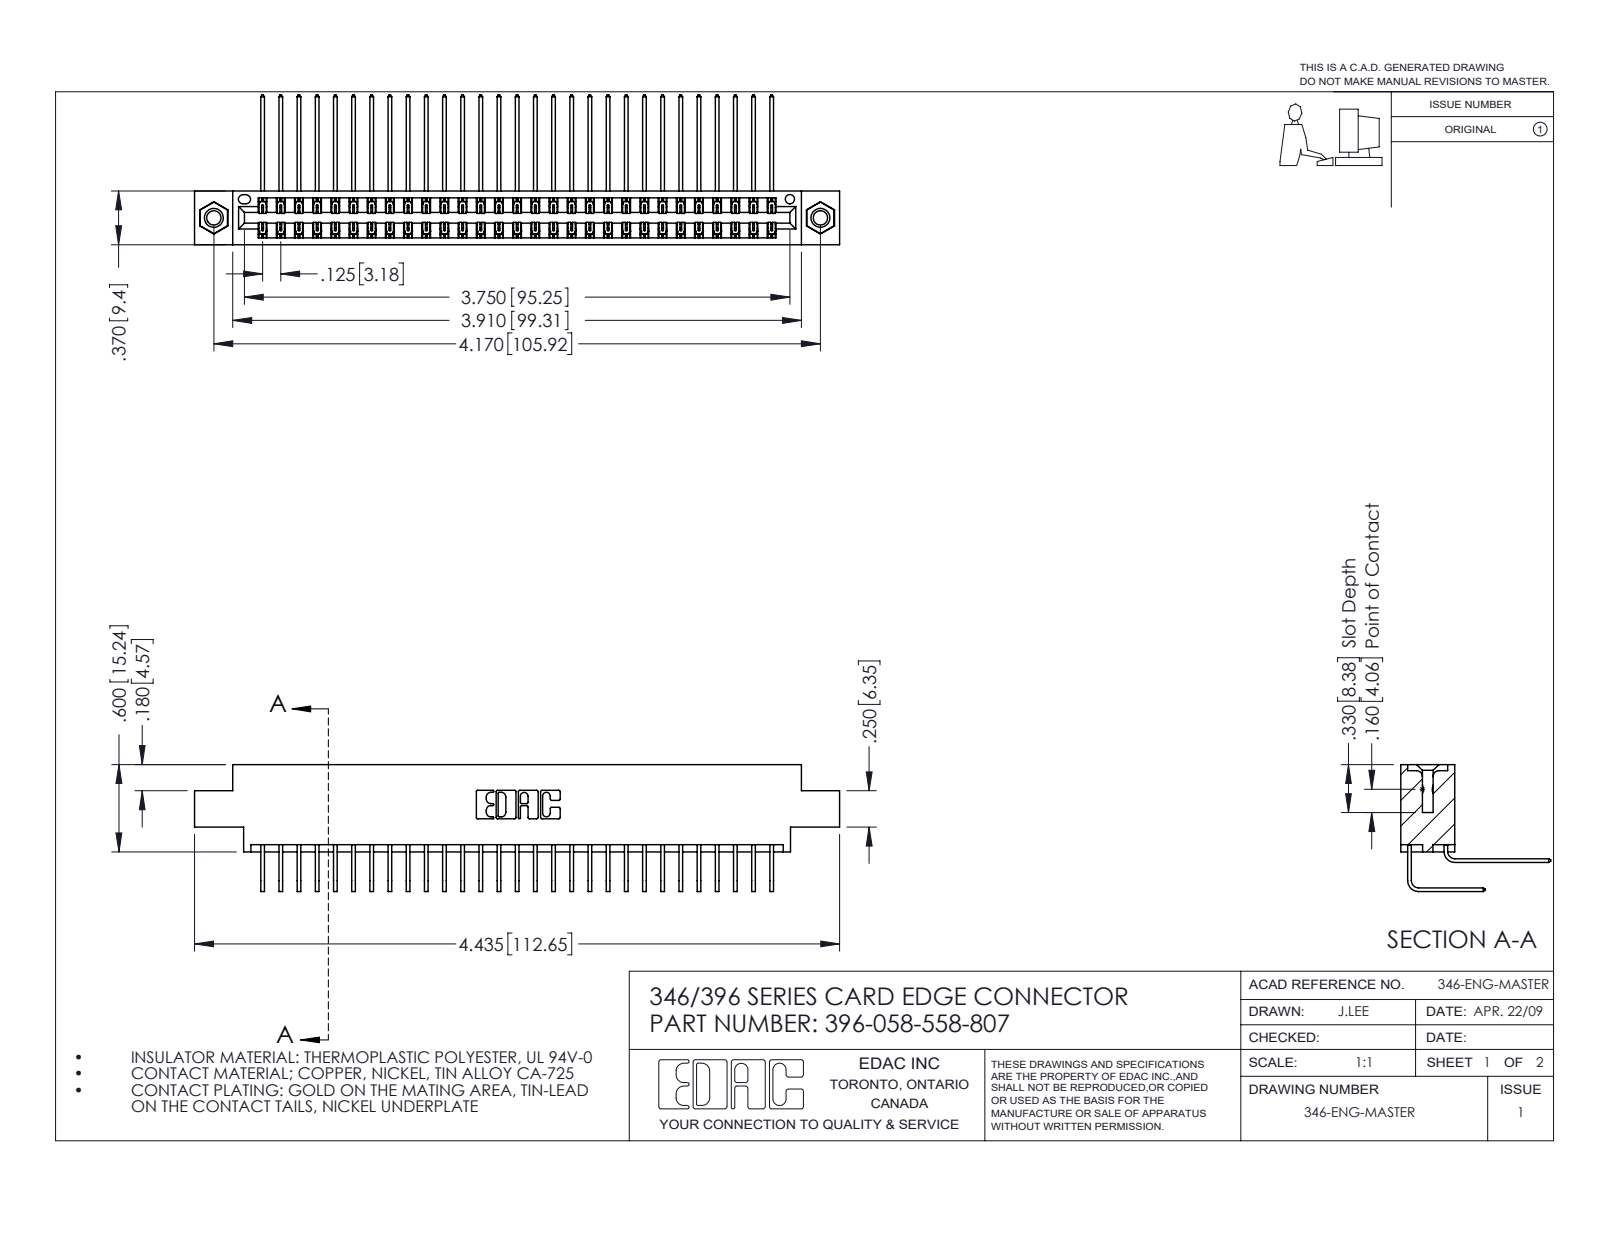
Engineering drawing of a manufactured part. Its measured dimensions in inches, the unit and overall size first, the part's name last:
Units: inches
Overall size (bounding box): 4.435 × 1.03 × 0.873
Round holes (diameter × count): ⌀0.098 ×2, ⌀0.125 ×2, ⌀0.156 ×2, ⌀0.064 ×1
Round bosses / shafts (diameter × count): ⌀0.155 ×2
Partial cylindrical surfaces — rounded edges, fillets, slot ends (radius × count): R0.006 ×87, R0.01 ×22, R0.007 ×6, R0.031 ×6, R0.026 ×3, R0.014 ×2, R0.022 ×2, R0.024 ×2
Main face-to-face distances: 0.322, 0.048, 0.025, 0.37, 0.25, 0.298, 0.072, 0.275, 0.222, 0.148
Hole centre spacings: 0.246, 3.962, 4.17
Volume: 0.674 in³ · Surface area: 26.05 in²
Bodies: 61 solids, 3318 faces (2258 planar, 1044 cylindrical, 16 other)
Part name (STEP PRODUCT): 396-058-558-807; 345-250-001_345-250-005-103; 345-292-001_558 Tail - 2; 346 Part_0.170 Offset - 0.156 Dia-TI (+1 more)
STEP written by: SolidWorks 2016 (CONFIG_CONTROL_DESIGN)
